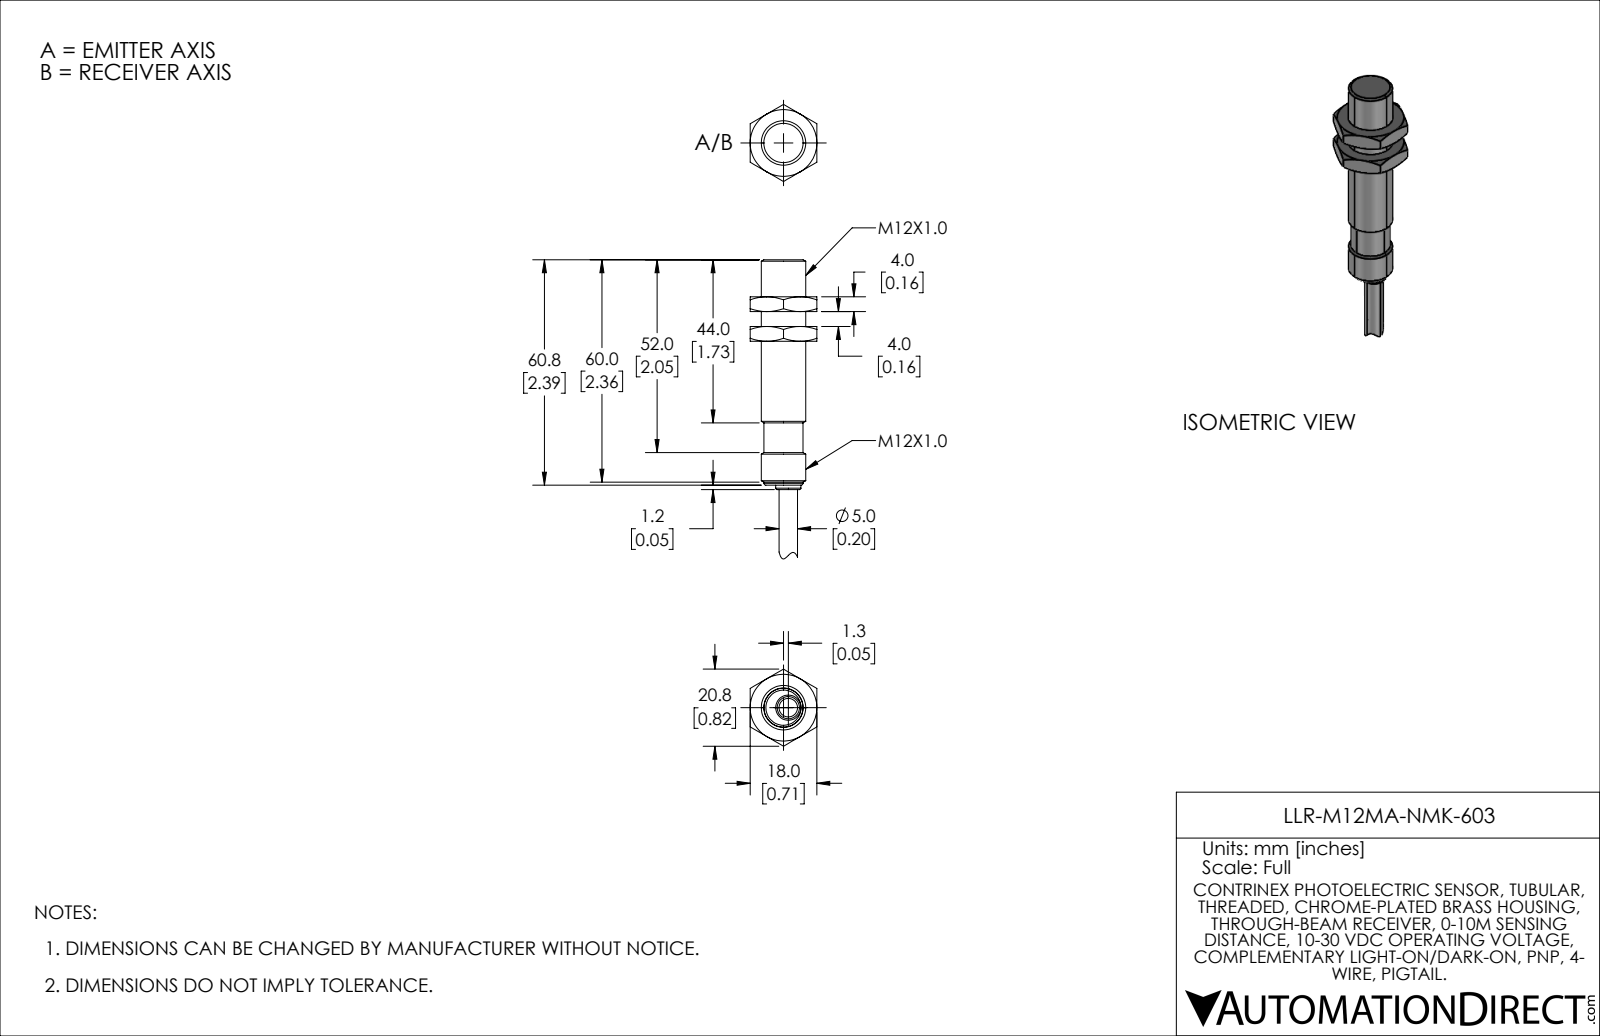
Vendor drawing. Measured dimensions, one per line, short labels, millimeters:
name: LLR-M12MA-NMK-603
written by: SolidWorks 2021 (AUTOMOTIVE_DESIGN)
unit: mm
bodies: 3 solids, 103 faces (20 planar, 29 cylindrical, 54 other)
size: 80.7 × 20.79 × 18
volume: 8 543 mm³; area: 4 229 mm²
holes: 1× ⌀10.2, 1× ⌀12
bosses: 1× ⌀10.55, 1× ⌀10.5, 1× ⌀6.8, 1× ⌀5
face distances: 4, 18, 8, 12, 10, 14, 22, 60.8, 50.8, 46.8
